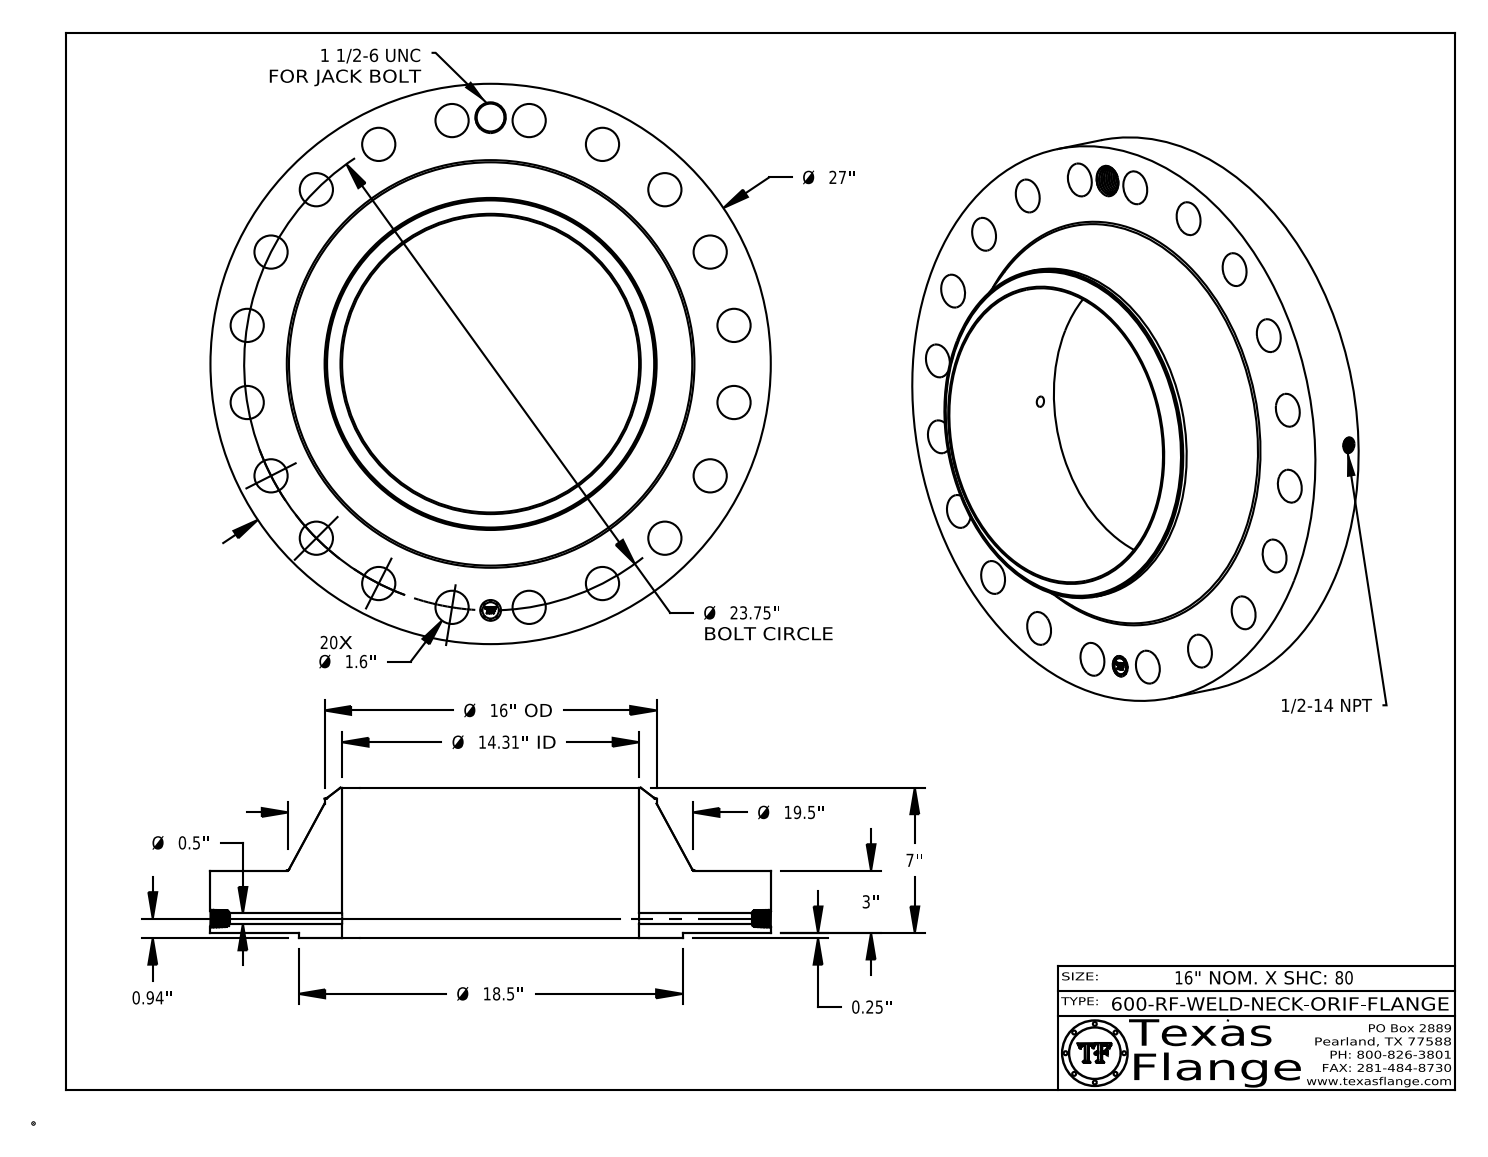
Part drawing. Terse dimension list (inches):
name: 600-RF-WELD-NECK
written by: CATIA V5 STEP AP214 (AUTOMOTIVE_DESIGN)
unit: in
bodies: 1 solid, 815 faces (369 planar, 124 cylindrical, 322 other)
size: 27 × 27 × 7.25
volume: 1 436 in³; area: 1 805 in²
holes: 20× ⌀1.6, 1× ⌀0.5, 1× ⌀0.672, 1× ⌀1, 1× ⌀1.344, 1× ⌀14.312
bosses: 8× ⌀0.061, 1× ⌀27, 1× ⌀18.5, 1× ⌀16, 1× ⌀0.788
face distances: 3, 0.25, 3.25, 7.25, 7, 4, 0.015, 3.235, 2.985, 4.015
hole spacings: 11.875, 16.794, 22.587, 23.457, 3.715, 13.96, 19.214, 7.339
